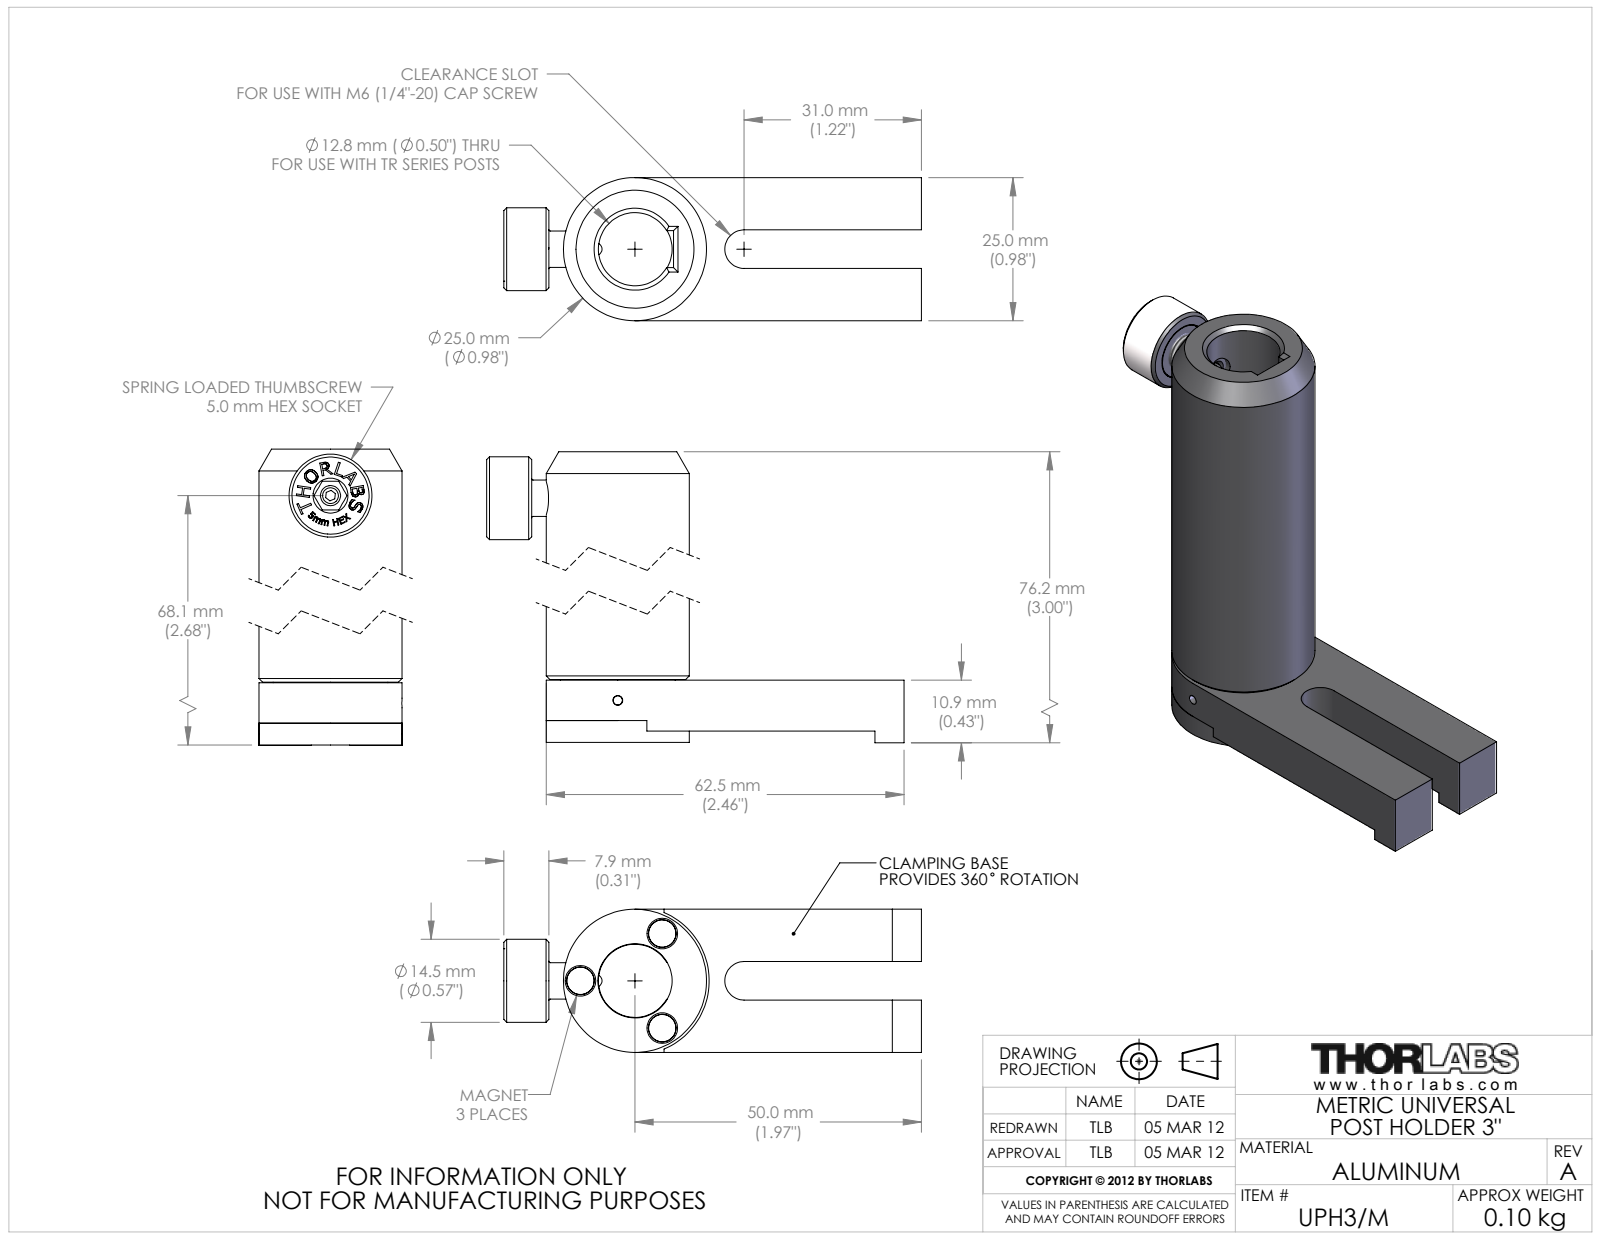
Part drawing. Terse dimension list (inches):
name: 21065-E0W
written by: SolidWorks 2011 (AUTOMOTIVE_DESIGN)
unit: in
bodies: 10 solids, 436 faces (211 planar, 84 cylindrical, 141 other)
size: 3.004 × 2.871 × 0.984
volume: 2.145 in³; area: 26.63 in²
holes: 3× ⌀0.19, 1× ⌀0.063, 1× ⌀0.067, 1× ⌀0.07, 1× ⌀0.084, 1× ⌀0.1, 1× ⌀0.125, 1× ⌀0.138, 1× ⌀0.201, 1× ⌀0.4, 1× ⌀0.503, 1× ⌀0.51
bosses: 3× ⌀0.187, 1× ⌀0.984, 1× ⌀0.79, 1× ⌀0.7, 1× ⌀0.68, 1× ⌀0.57, 1× ⌀0.39, 1× ⌀0.25
rounds: 1× R0.133, 1× R0.51
face distances: 0.35, 0.359, 0.625, 0.984, 0.072, 0.278, 0.078, 0.15, 0.428, 0.265
hole spacings: 0.375, 0.649, 0.65, 2.377
